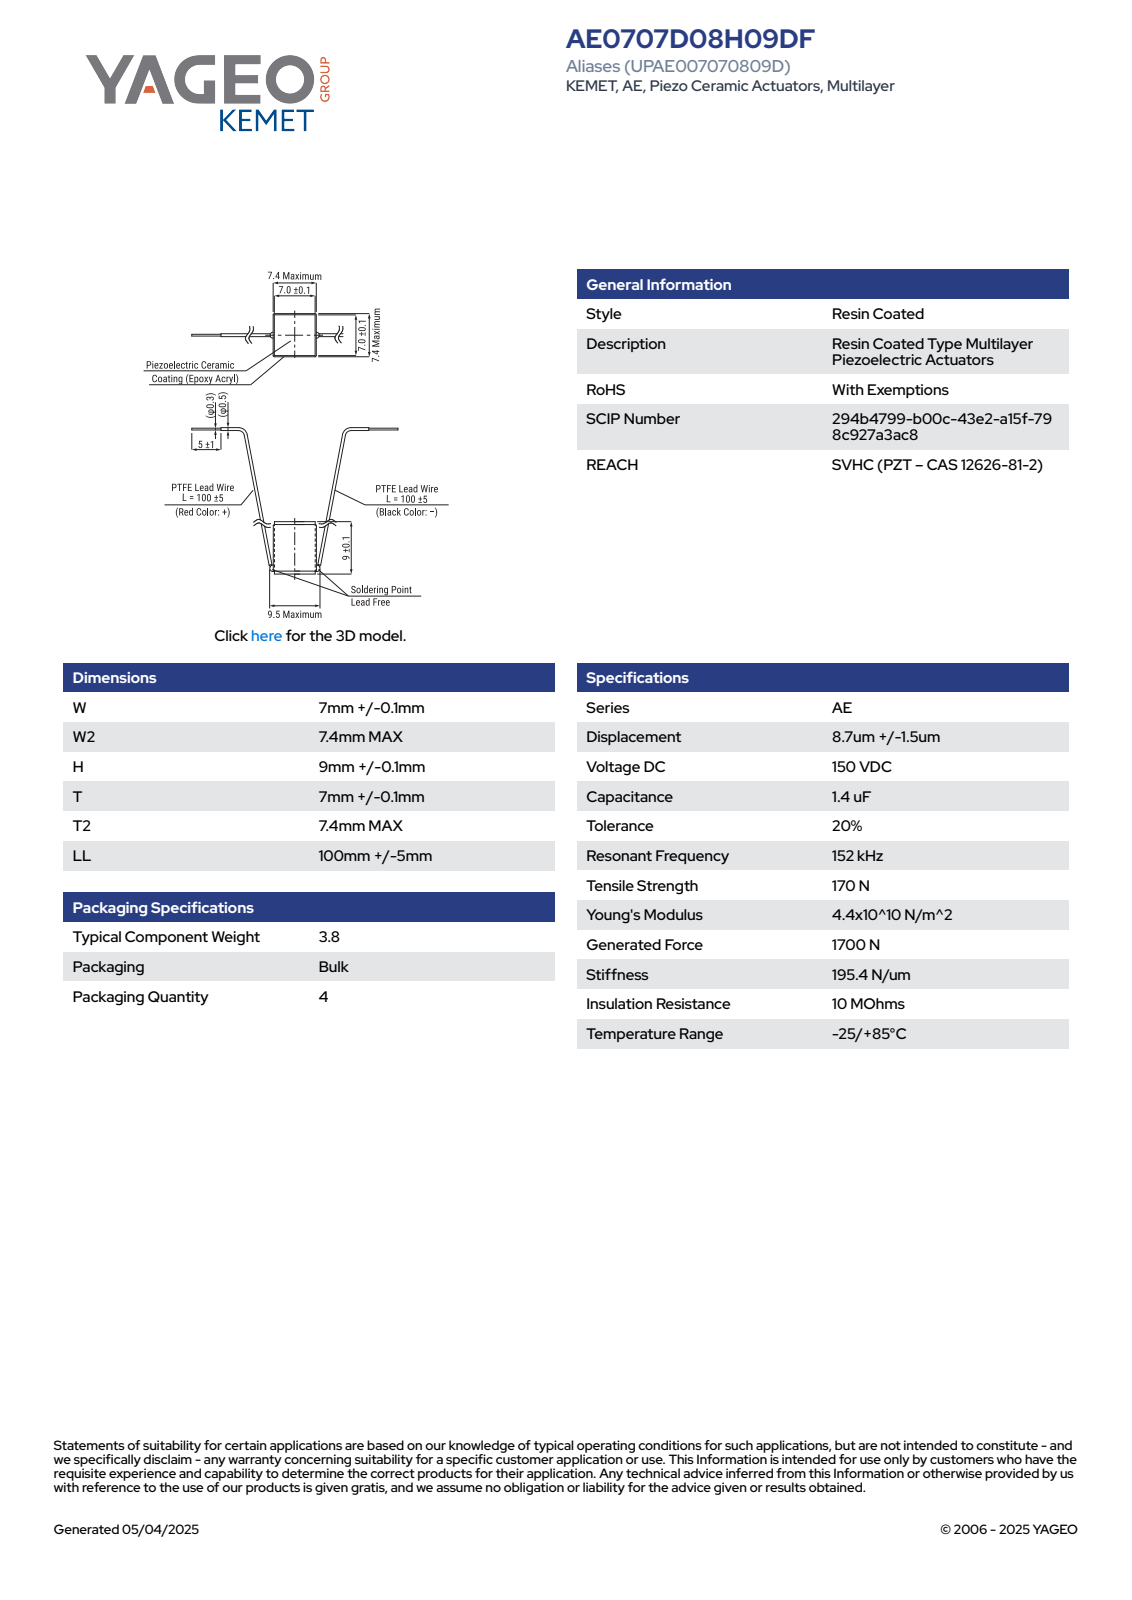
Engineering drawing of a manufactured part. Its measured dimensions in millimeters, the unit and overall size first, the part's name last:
Units: millimetres
Overall size (bounding box): 9.11 × 7.4 × 7.4
Partial cylindrical surfaces — rounded edges, fillets, slot ends (radius × count): R0.15 ×8
Main face-to-face distances: 7.1, 7.25, 9.1, 7, 6.9, 7.4, 3.66, 5.44, 0.89, 8.21
Volume: 459 mm³ · Surface area: 384 mm²
Bodies: 4 solids, 93 faces (85 planar, 8 cylindrical, 0 other)
Part name (STEP PRODUCT): AL_KAE1_W7.1W27.4H9.1T7.1T27.4
STEP written by: SolidWorks 2014 (AUTOMOTIVE_DESIGN)
